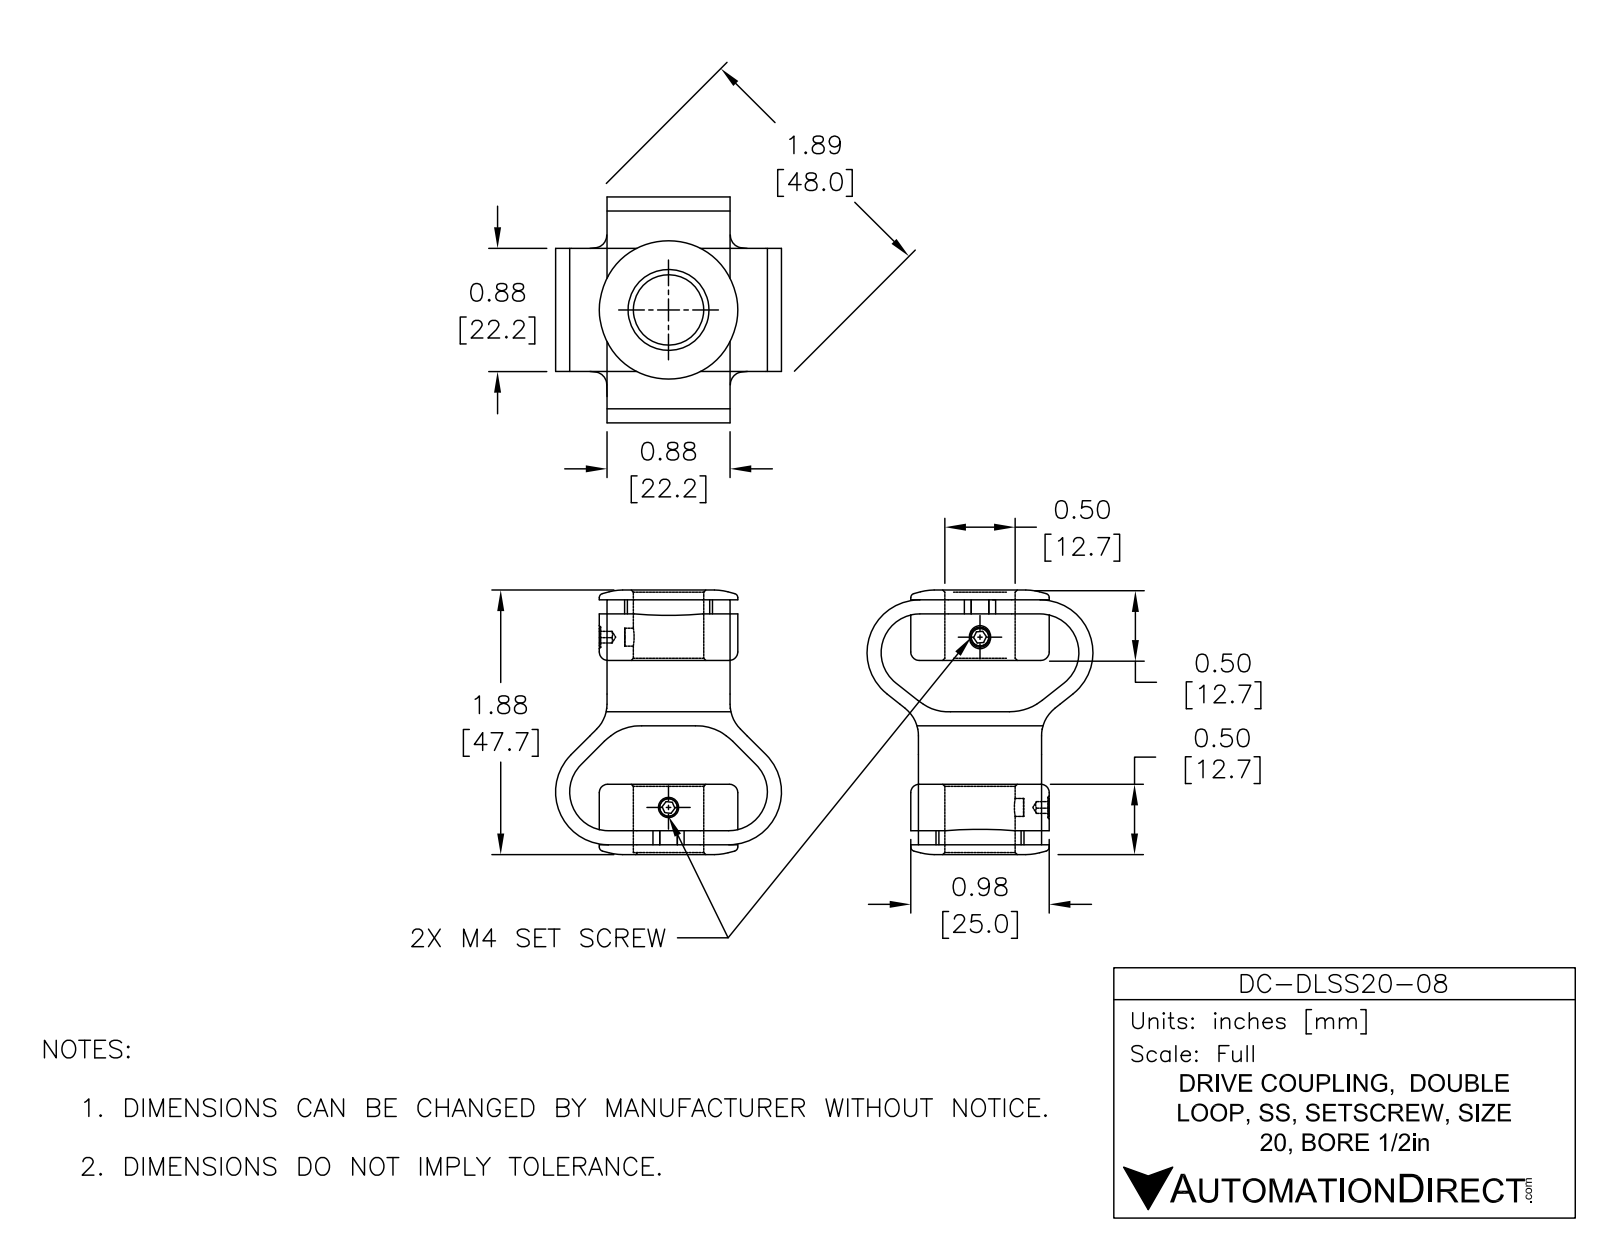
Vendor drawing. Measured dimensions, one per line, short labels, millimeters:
name: DC-DLSS20-08
written by: SolidWorks 2015 (AUTOMOTIVE_DESIGN)
unit: mm
bodies: 1 solid, 173 faces (90 planar, 47 cylindrical, 36 other)
size: 47.75 × 40.77 × 40.77
volume: 16 258 mm³; area: 11 312 mm²
holes: 2× ⌀3.24, 1× ⌀12.7
bosses: 1× ⌀25
rounds: 7× R9.53, 6× R6.35, 4× R6.99, 3× R1.91, 1× R1.91, 1× R7.94
face distances: 2.54, 12.7, 35.05, 1.78, 45.97, 10.92, 33.27, 9.27, 13.08, 22.35
